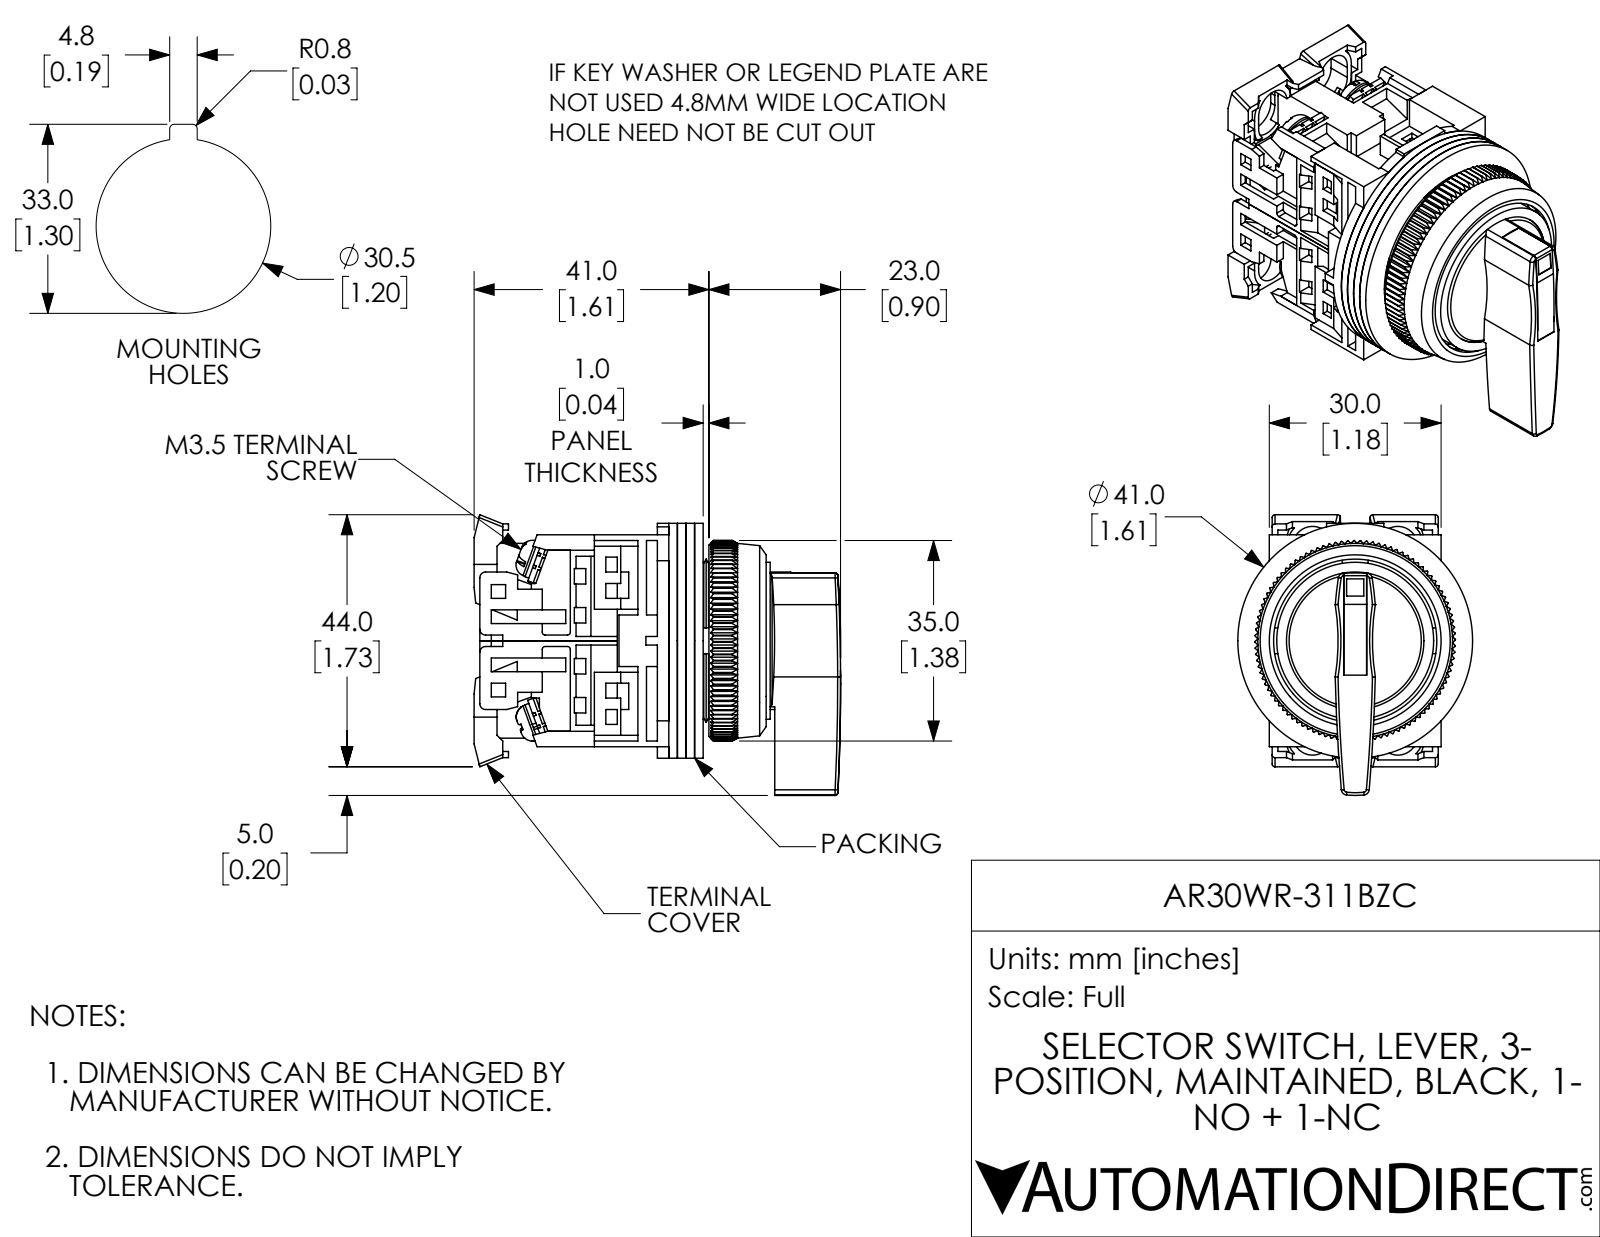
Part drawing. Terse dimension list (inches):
name: AR30WR-311BZC
written by: SolidWorks 2017 (AUTOMOTIVE_DESIGN)
unit: in
bodies: 26 solids, 1818 faces (1288 planar, 287 cylindrical, 243 other)
size: 2.52 × 1.929 × 1.614
volume: 2.333 in³; area: 62.88 in²
holes: 8× ⌀0.138, 4× ⌀0.142, 1× ⌀0.118, 1× ⌀0.315, 1× ⌀0.472, 1× ⌀0.48, 1× ⌀0.512, 1× ⌀0.819, 1× ⌀0.945, 1× ⌀1.122, 1× ⌀1.181, 1× ⌀1.252
bosses: 4× ⌀0.26, 4× ⌀0.138, 1× ⌀1.614, 1× ⌀1.15, 1× ⌀1.079, 1× ⌀0.787, 1× ⌀0.709, 1× ⌀0.669
rounds: 16× R0.059, 13× R0.02, 8× R0.039, 4× R0.138, 4× R0.177, 2× R0.118, 2× R1.575, 2× R1.638
face distances: 0.059, 0.118, 0.177, 0.039, 0.079, 1.417, 0.197, 1.358, 0.512, 0.213
hole spacings: 0.579, 0.61
